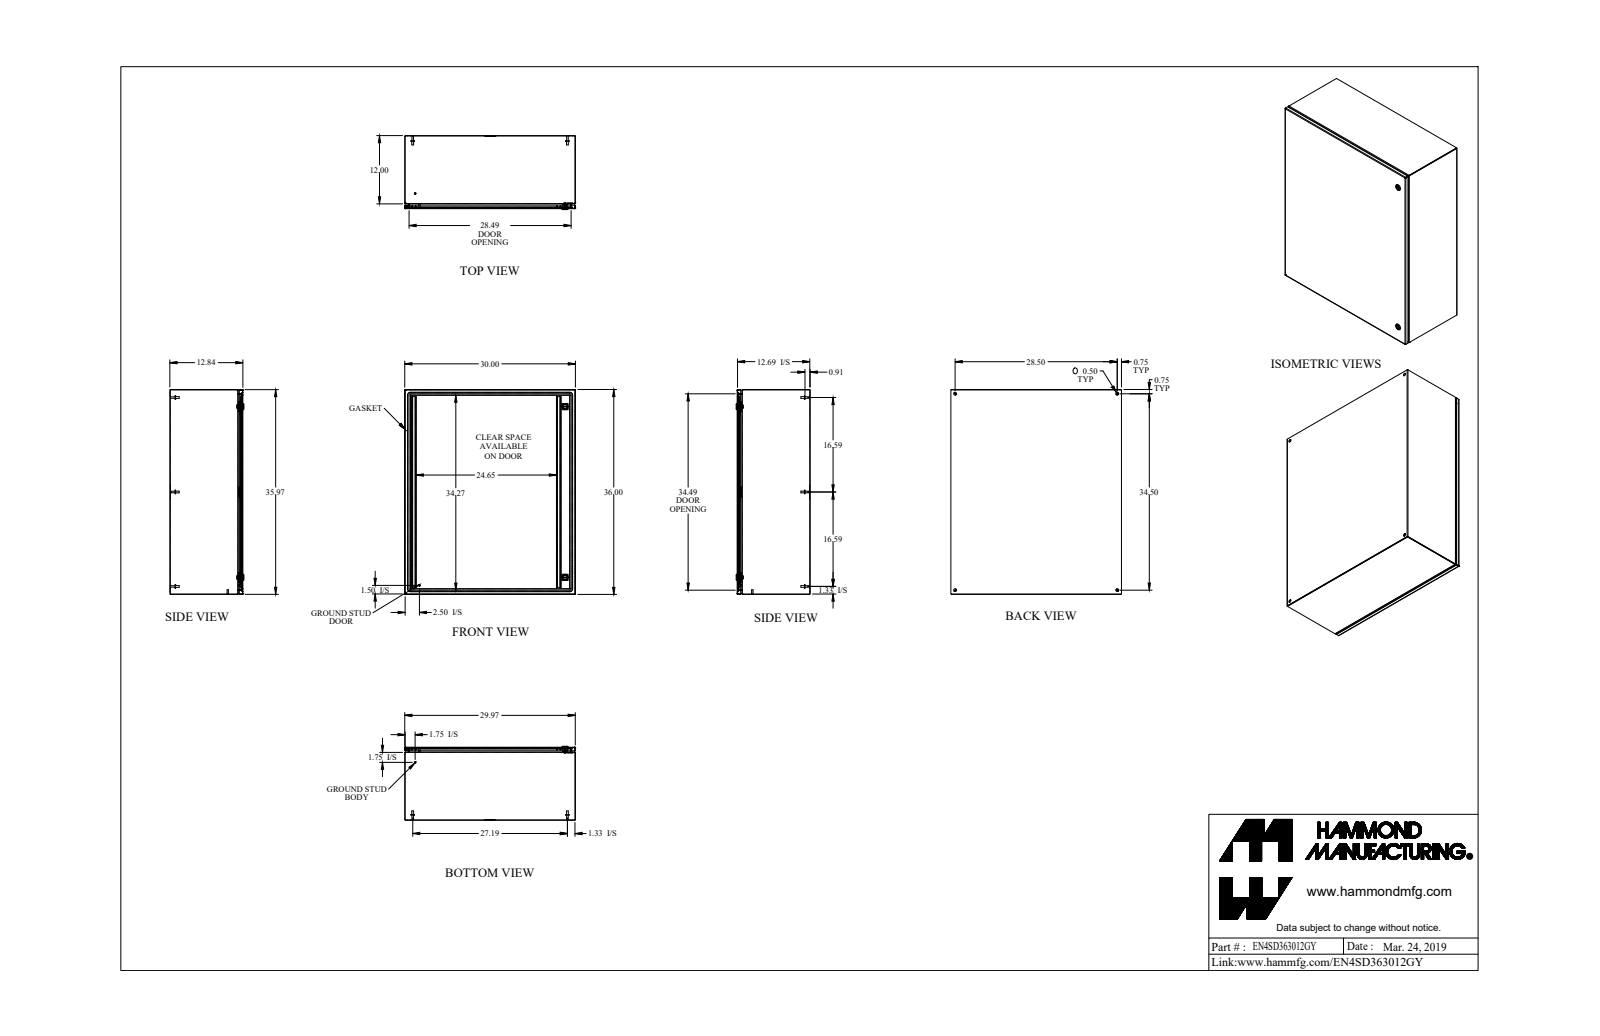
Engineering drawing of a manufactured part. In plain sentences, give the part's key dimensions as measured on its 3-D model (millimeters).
The part is named "EN4SD363012GY". Its 3-D file was written by "SolidWorks 2019 (AUTOMOTIVE_DESIGN)". It is 35 solids with 901 faces: 434 planar, 295 cylindrical and 172 other. Overall it measures 914.4 by 762 by 330.1 millimeters. Its volume is 5 003 000 cubic millimeters and its surface area 5 521 000 square millimeters. Round holes: 4 of diameter 12.7, 2 of diameter 5.9, 2 of diameter 15.9, 2 of diameter 19.9, 1 of diameter 4.4, 1 of diameter 6.1, 1 of diameter 6.1. Round bosses or shafts: 6 of diameter 15.9, 6 of diameter 8, 6 of diameter 6.9, 2 of diameter 27.9, 2 of diameter 13.3, 2 of diameter 7.1, 2 of diameter 6.4, 1 of diameter 11.6. Partial cylindrical surfaces (rounded edges, fillets, slot ends): 18 of radius 0.9, 18 of radius 2.7, 12 of radius 1.1, 12 of radius 2.1, 12 of radius 7.9, 6 of radius 0.2, 6 of radius 1.6, 4 of radius 3.2. The main face-to-face distances are 1.8, 324.2, 322.4, 326.1, 760.2, 912.6, 758.3, 762, 910.7, 914.4. The hole center spacings are 699, 723.9, 876.3, 1136.6, 63.3, 63.3, 762, 819.6.
